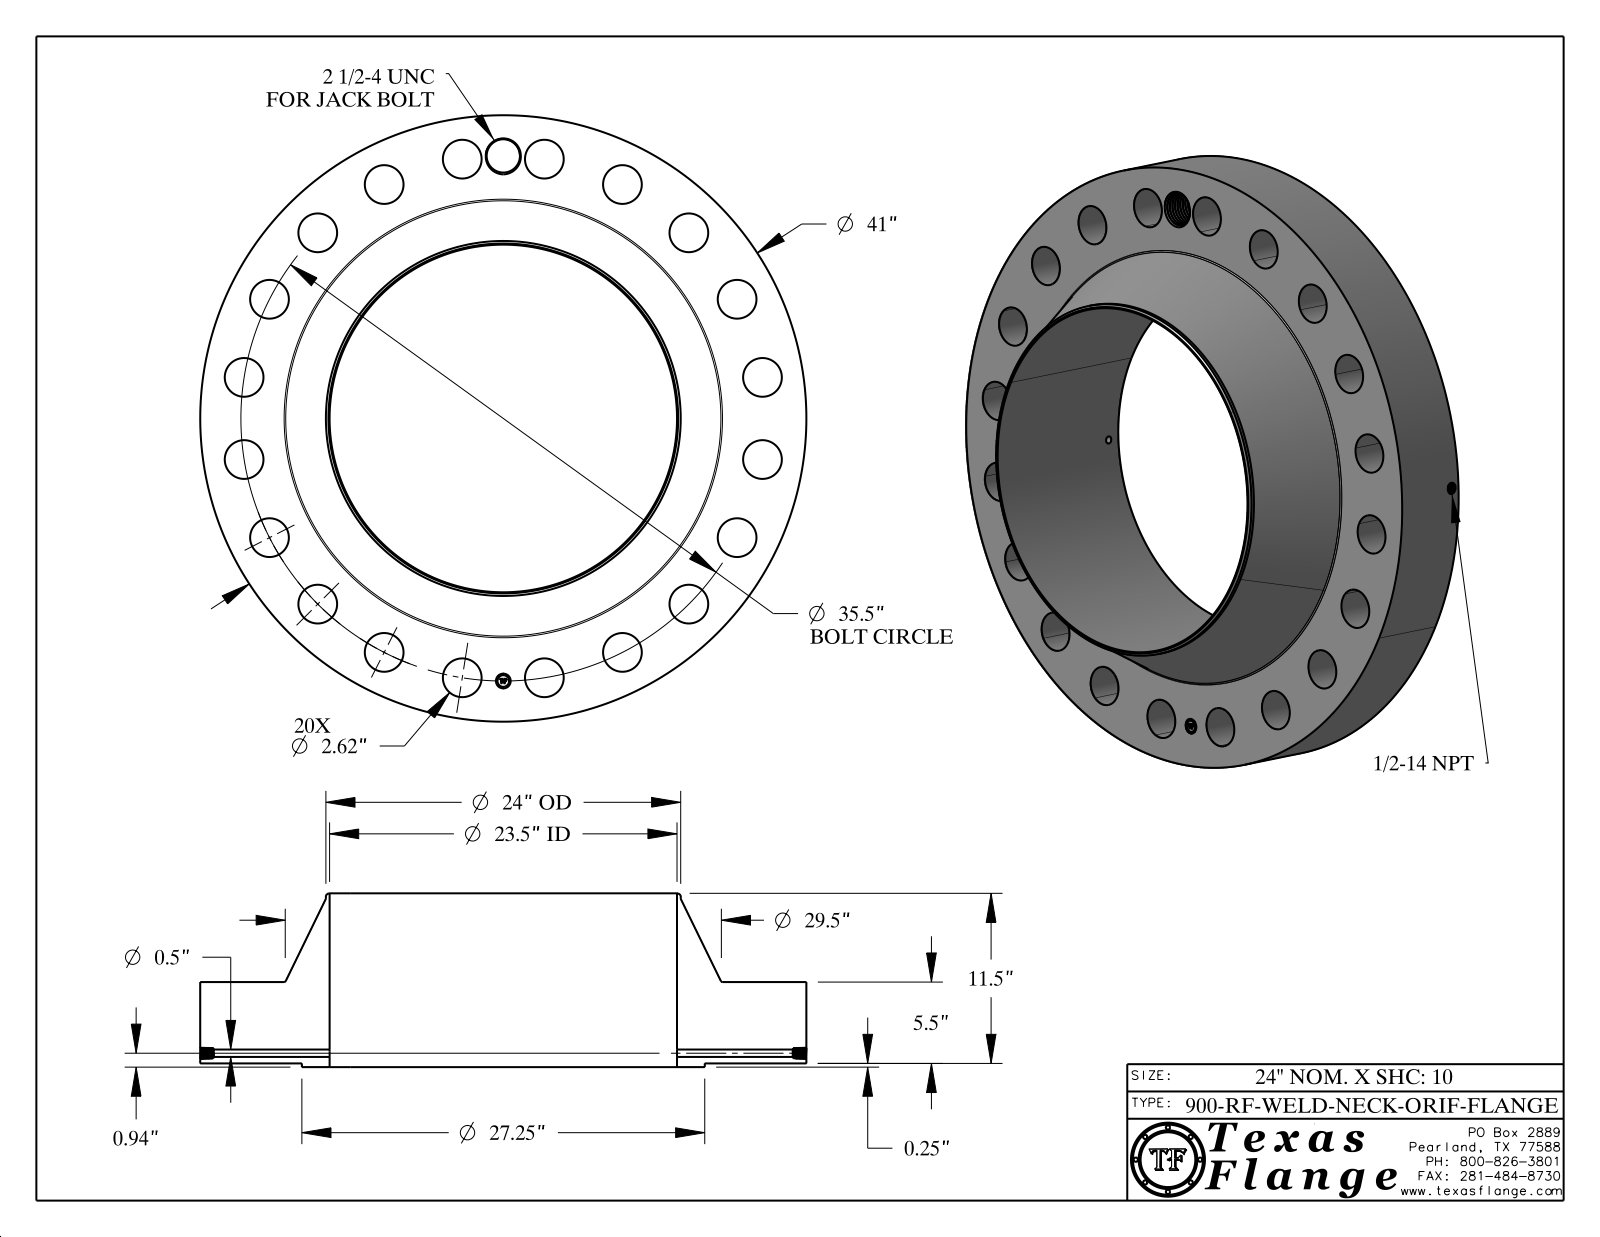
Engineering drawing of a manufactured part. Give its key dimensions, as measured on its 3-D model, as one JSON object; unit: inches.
{"part_name": "900-RF-WELD-NECK", "step_written_by": "CATIA V5 STEP AP214 (AUTOMOTIVE_DESIGN)", "units": "inches", "bodies": {"solids": 1, "faces": 835, "planar": 369, "cylindrical": 132, "other": 334}, "overall_size": [41, 41, 11.75], "volume_in3": 5032, "surface_area_in2": 4456, "round_holes": [[2.62, 20], [0.5, 1], [0.672, 1], [1, 1], [2.25, 1], [23.5, 1]], "round_bosses_or_shafts": [[0.061, 8], [41, 1], [27.25, 1], [24, 1], [0.788, 1]], "face_to_face_distances": [5.5, 0.25, 5.75, 11.75, 11.5, 6, 5.735, 5.485, 0.015, 6.015], "hole_center_spacings": [17.75, 10.97, 25.102, 28.72, 31.631, 35.063, 20.867, 33.763]}
